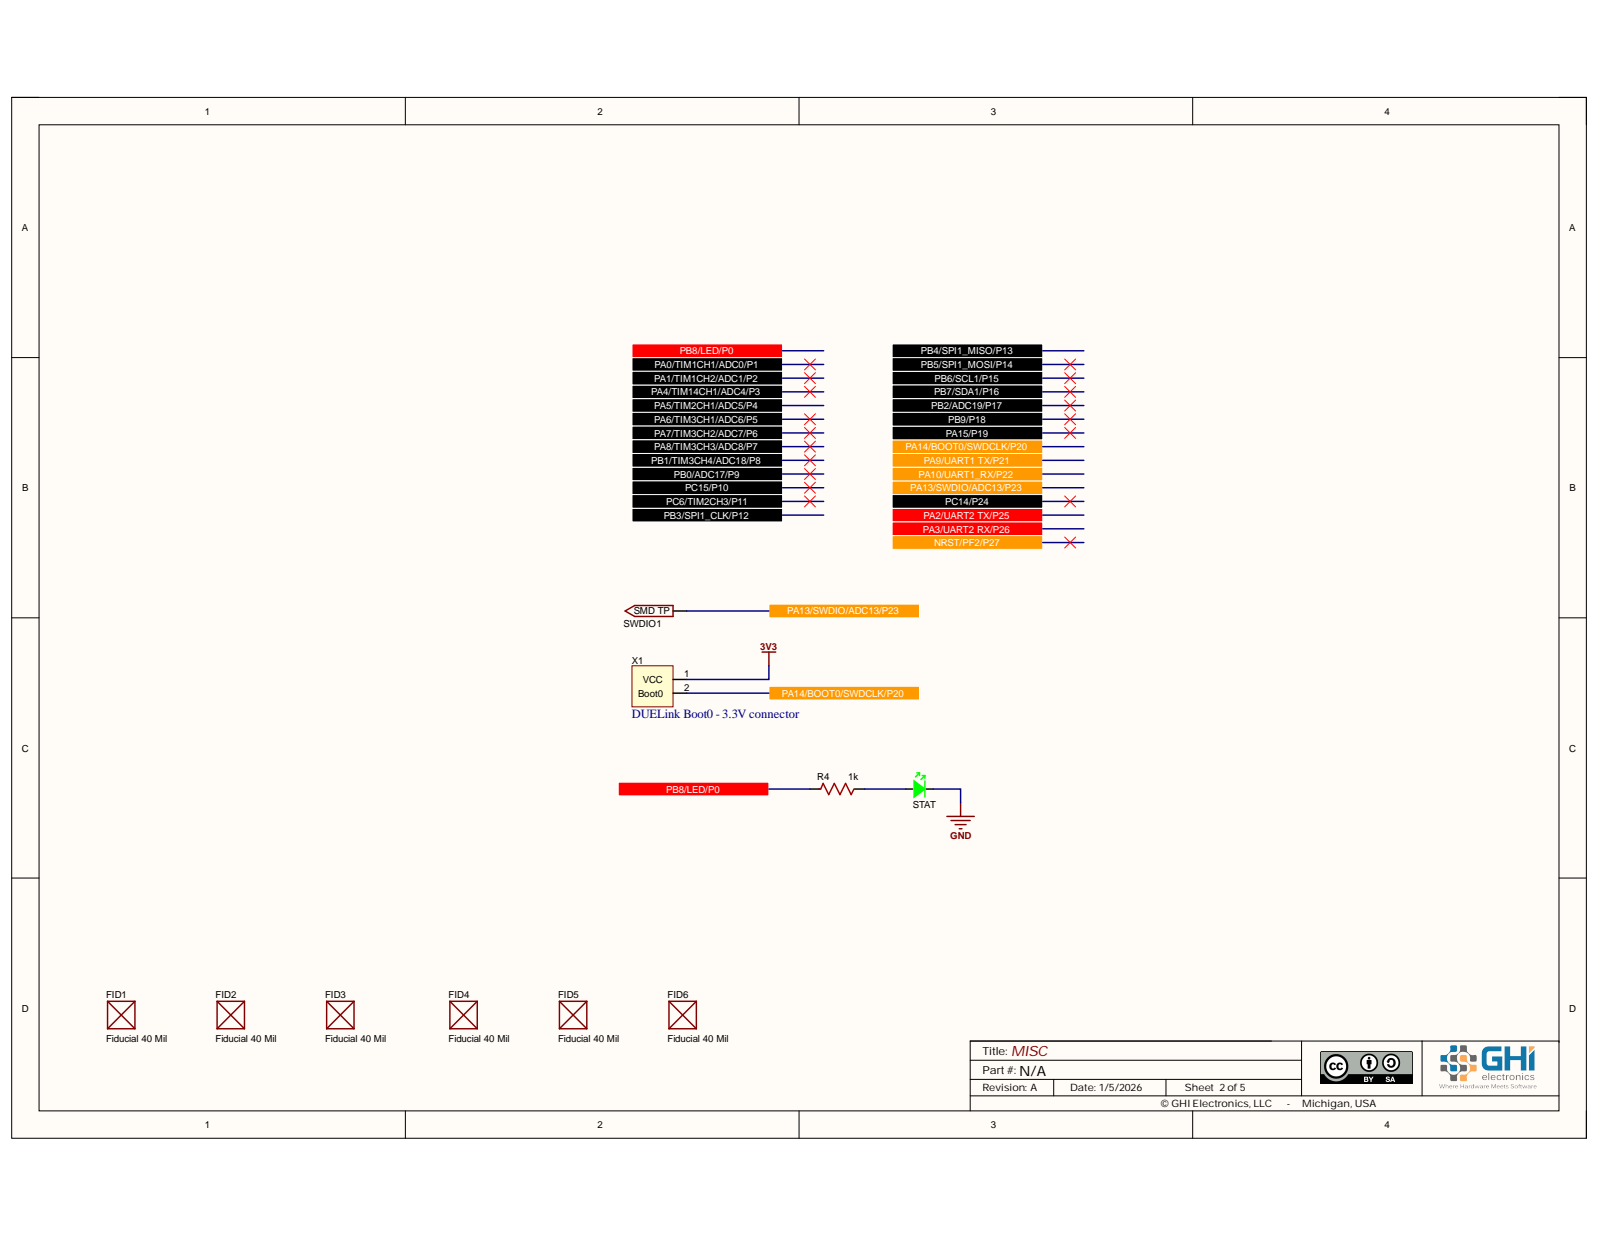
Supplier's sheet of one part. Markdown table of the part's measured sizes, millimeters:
| quantity | value |
| --- | --- |
| part name | PCB; Board; J3; Conn_Molex_22-28-6054_eec (+5 more) |
| STEP written by | Open CASCADE 7.5 (AUTOMOTIVE_DESIGN) |
| units | millimeters |
| bodies | 145 solids, 2677 faces (1682 planar, 586 cylindrical, 409 other) |
| overall size | 100.53 × 58.53 × 19.76 |
| volume | 6 166 mm³ |
| surface area | 15 001 mm² |
| round holes (diameter × count) | 0.9 × 5, 1.02 × 5, 1.8 × 5, 2.5 × 4, 3 × 4, 1.02 × 2, 1.5 × 2, 3.32 × 2, 4.25 × 2, 4.32 × 2, 0.5 × 1, 3.7 × 1 |
| round bosses / shafts (diameter × count) | 1.3 × 6, 5.6 × 2, 4.6 × 2, 4 × 2, 3 × 2, 5.9 × 1, 4.4 × 1, 3.78 × 1 |
| partial cylindrical surfaces (radius × count) | 0.12 × 35, 0.4 × 18, 0.15 × 14, 0.25 × 8, 0.3 × 8, 0.1 × 4, 0.2 × 4, 0.35 × 4 |
| main face-to-face distances | 1.08, 1, 4.02, 3.02, 2.94, 2.82, 3.82, 2.74, 1.16, 4.1 |
| hole center spacings | 2.54, 5.08, 7.62, 10.16, 24.22, 24.29, 28.76, 28.83 |
